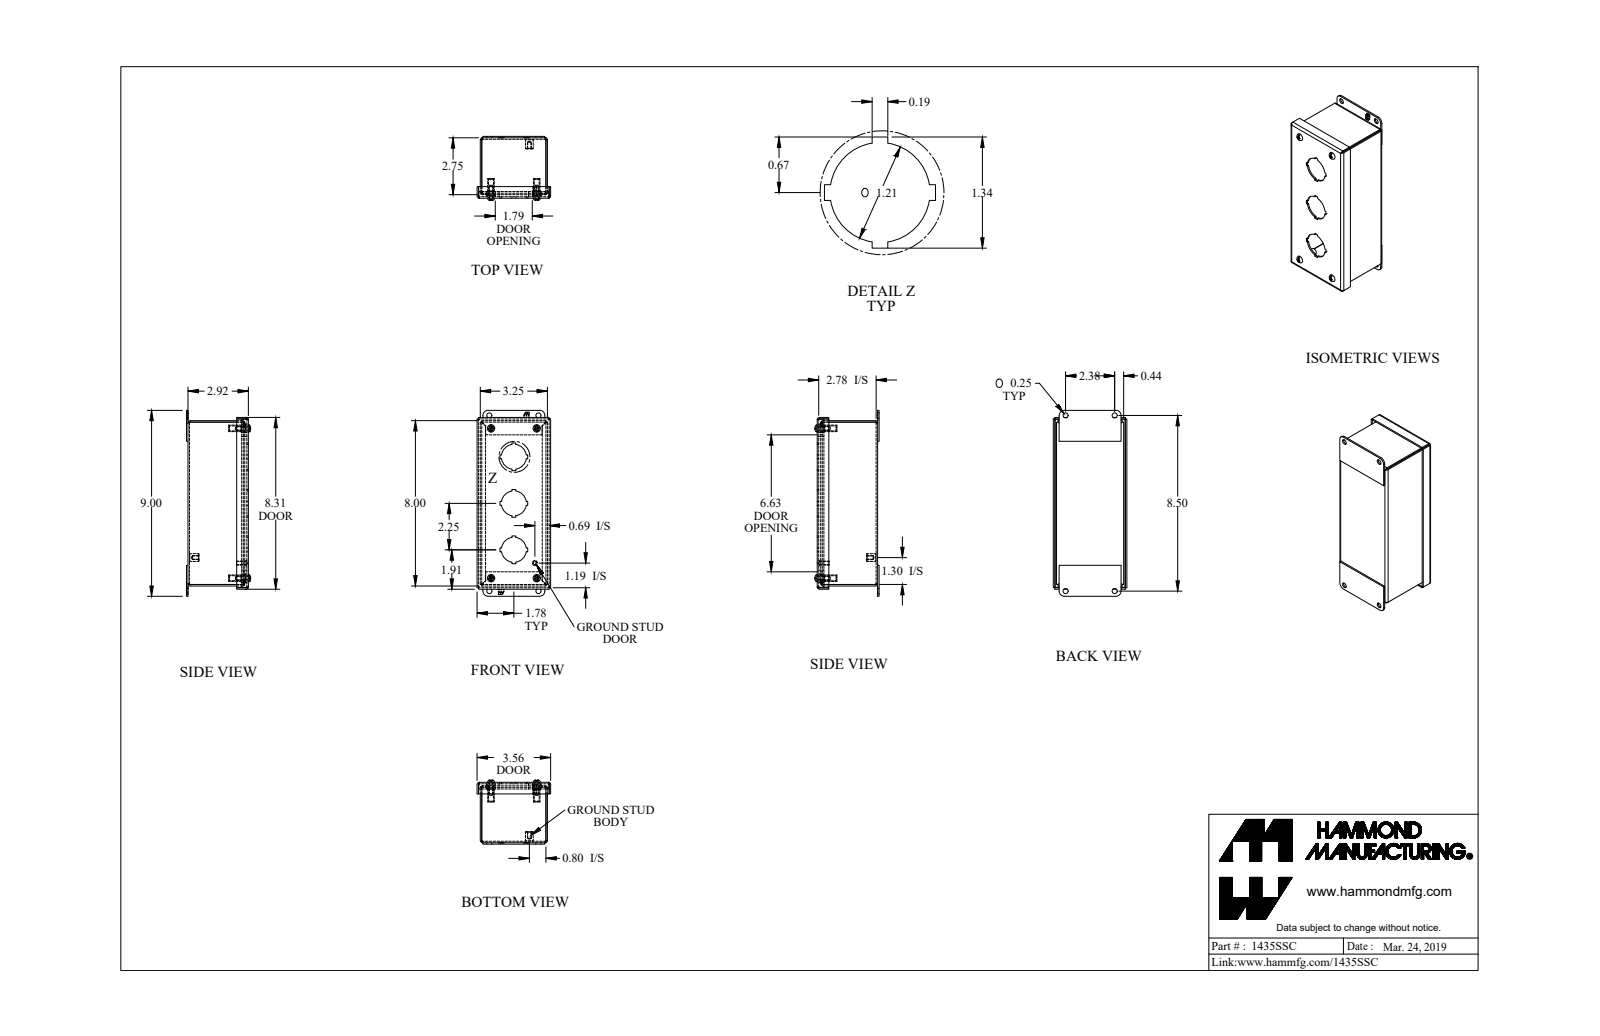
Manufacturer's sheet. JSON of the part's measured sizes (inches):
{"part_name": "1435SSC_Default", "step_written_by": "SolidWorks 2019 (CONFIG_CONTROL_DESIGN)", "units": "inches", "bodies": {"solids": 19, "faces": 493, "planar": 319, "cylindrical": 144, "other": 30}, "overall_size": [9, 3.562, 3.104], "volume_in3": 12.11, "surface_area_in2": 317.5, "round_holes": [[0.25, 8], [0.065, 4], [0.239, 4], [0.253, 4], [0.406, 4], [1.21, 3], [0.156, 1]], "round_bosses_or_shafts": [[0.19, 5], [0.406, 4], [0.315, 4], [0.148, 4], [0.375, 1], [0.25, 1]], "partial_cylinders_radius": [[0.036, 12], [0.108, 12], [0.171, 4], [0.25, 4], [0.125, 1]], "face_to_face_distances": [0.072, 2.85, 0.072, 3.178, 2.922, 2.778, 3.106, 3.25, 7.928, 0.156], "hole_center_spacings": [2.211, 7.25, 7.876, 2.212, 0.63, 0.63, 2.377, 3.791]}
